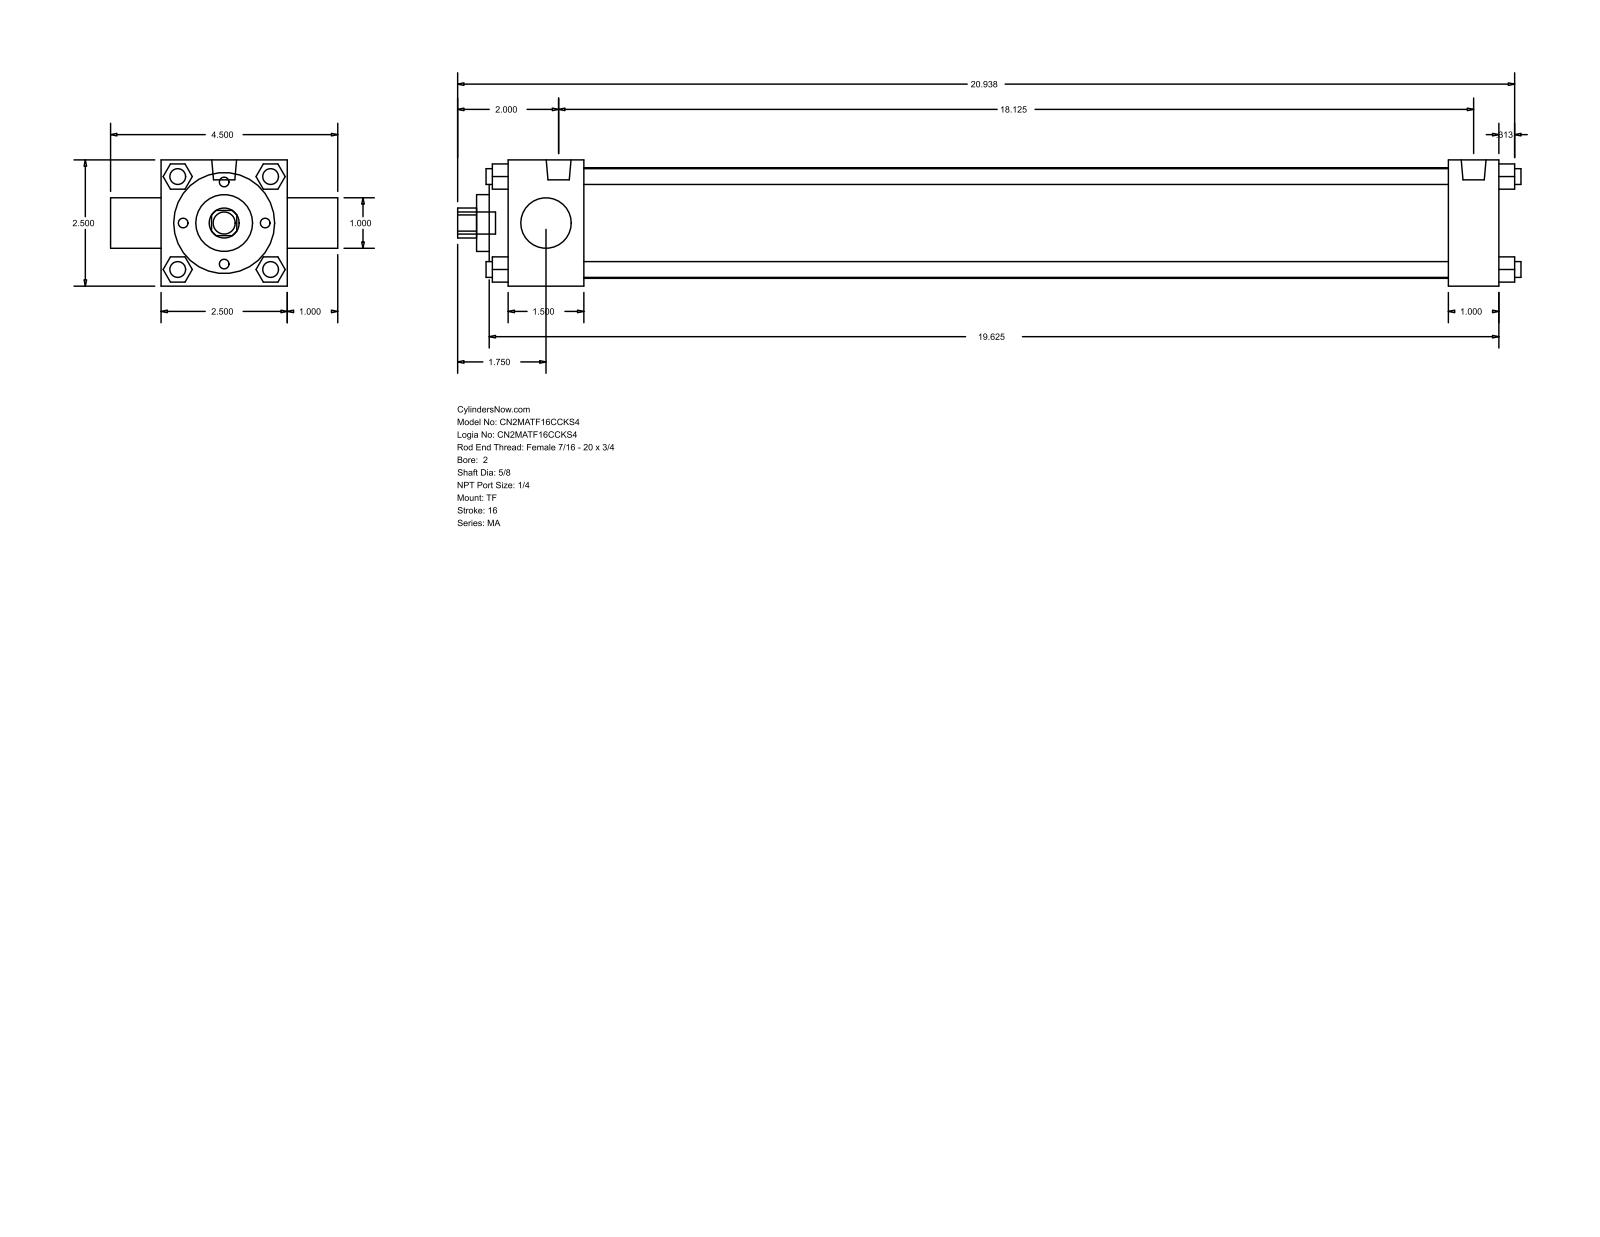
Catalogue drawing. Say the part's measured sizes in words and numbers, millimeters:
The part is named "MA_TF__0200_0.625". Its 3-D file was written by "GSSL Pune (CONFIG_CONTROL_DESIGN)". It is 0 solids with 122 faces: 93 planar, 29 cylindrical and 0 other. Overall it measures 534.99 by 114.3 by 63.5 millimeters. Round holes: 1 of diameter 15.88, 1 of diameter 25.4, 1 of diameter 28.57, 1 of diameter 50.8, 1 of diameter 55.63. Round bosses or shafts: 7 of diameter 7.94, 2 of diameter 12.49, 1 of diameter 11.11. Partial cylindrical surfaces (rounded edges, fillets, slot ends): 1 of radius 7.54. The main face-to-face distances are 63.5, 25.4, 38.1, 12.7, 498.48, 9.52, 473.08, 434.98, 460.38, 47.62.
